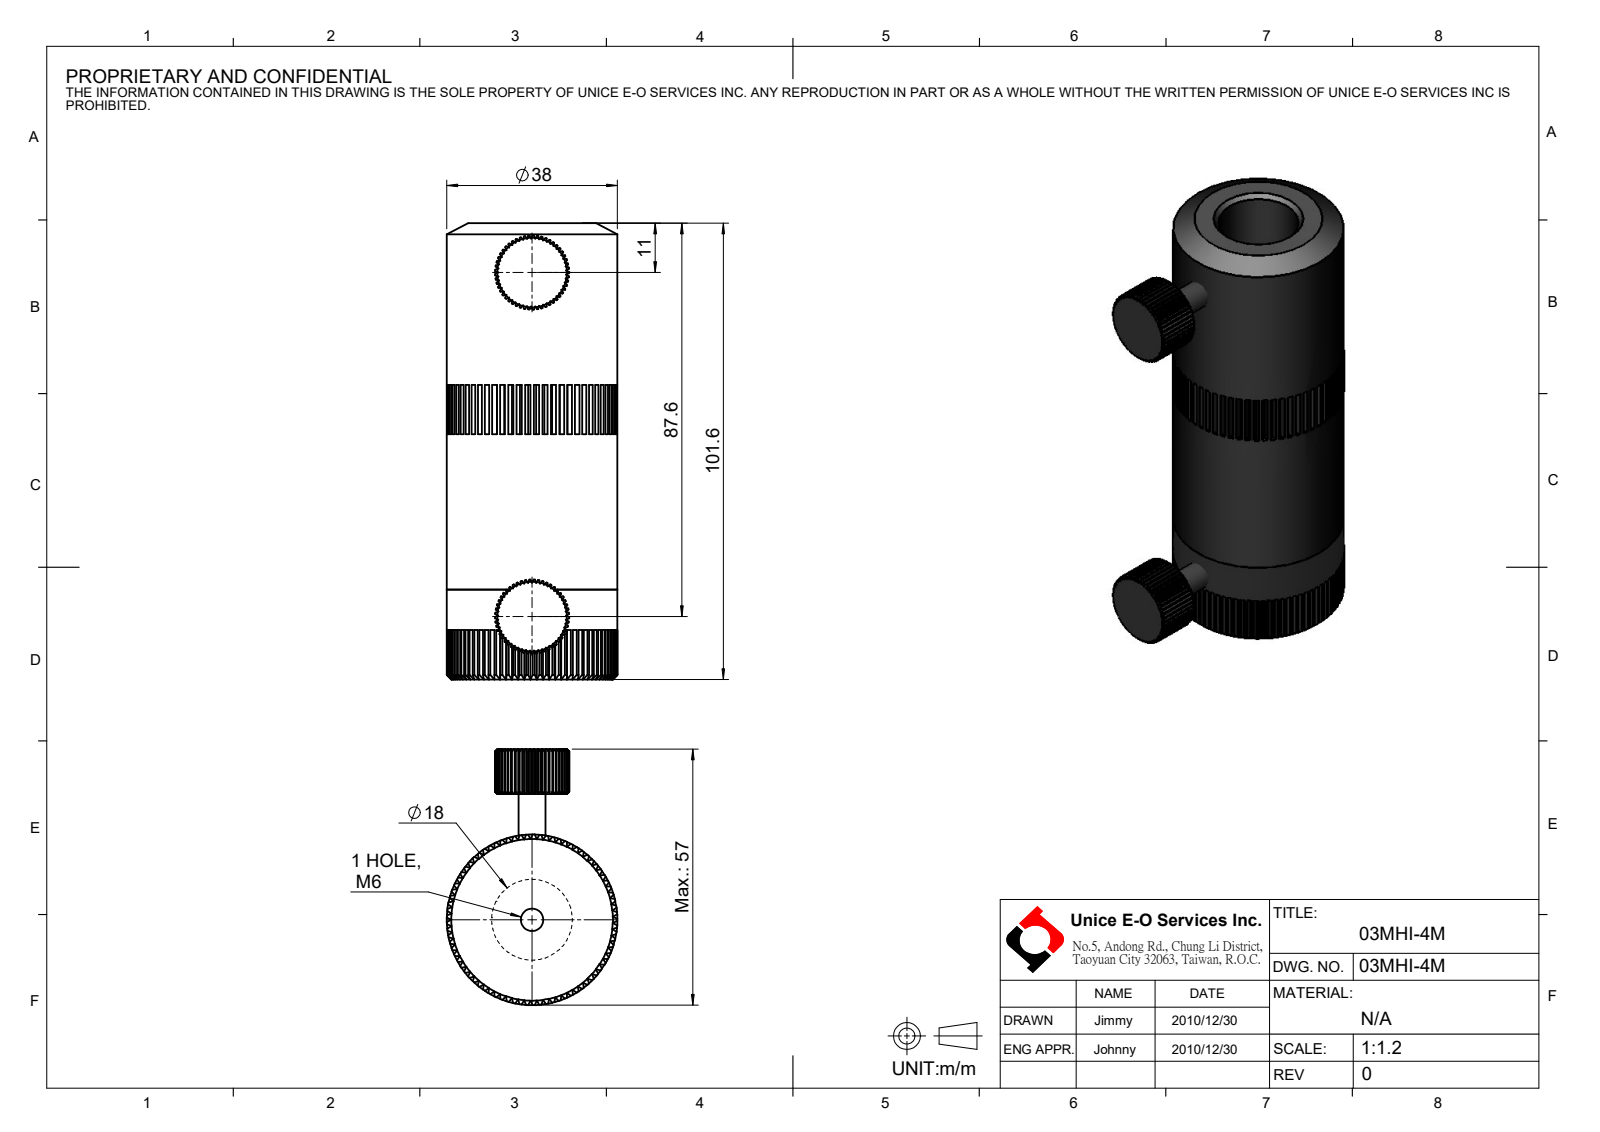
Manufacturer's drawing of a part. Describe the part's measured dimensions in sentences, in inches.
The part is named "03MHI-4M". Its 3-D file was written by "SolidWorks 2016 (CONFIG_CONTROL_DESIGN)". It is 0 solids with 1132 faces: 711 planar, 120 cylindrical and 301 other. Overall it measures 4 by 2.244 by 1.496 inches. Round holes: 2 of diameter 0.197, 1 of diameter 0.709. Round bosses or shafts: 2 of diameter 0.236, 1 of diameter 1.496. Partial cylindrical surfaces (rounded edges, fillets, slot ends): 2 of radius 0.325. The main face-to-face distances are 0.787, 0.631, 0.632, 4, 3.213, 0.394, 0.433, 2.15, 0.635, 0.631.
